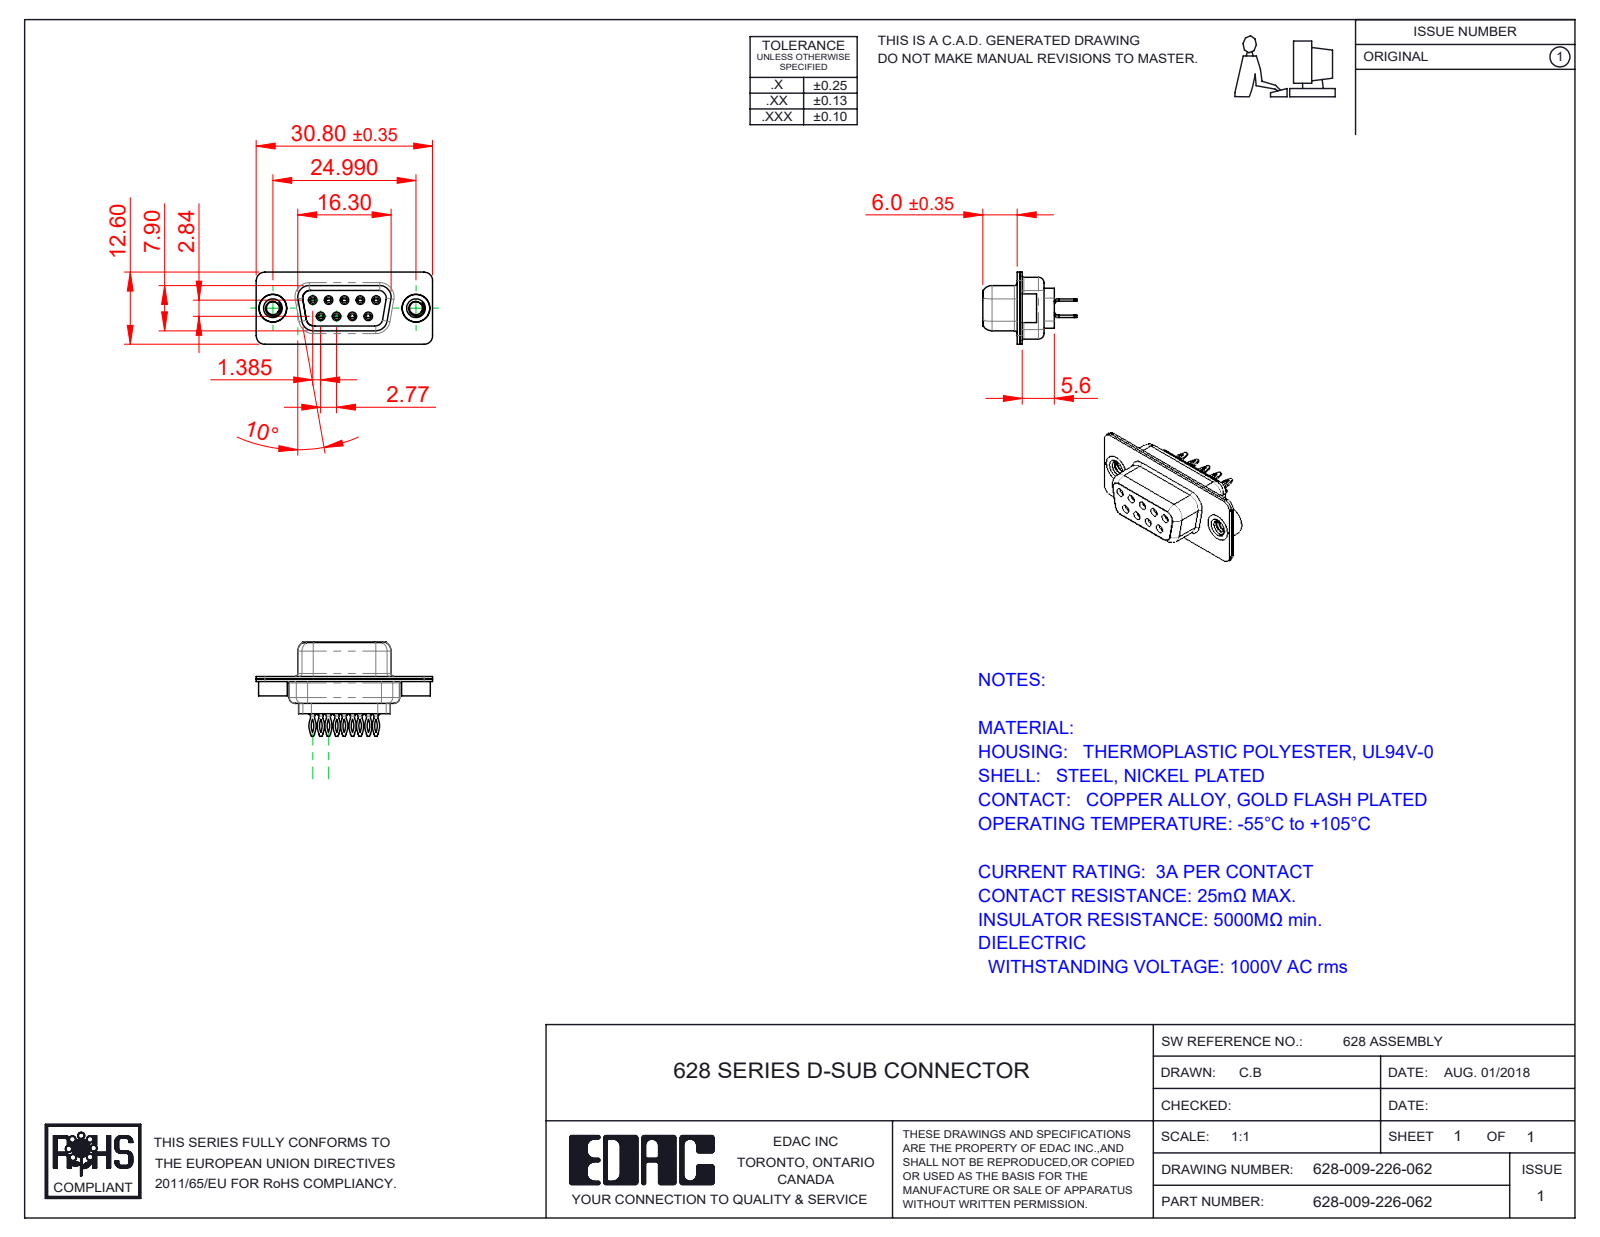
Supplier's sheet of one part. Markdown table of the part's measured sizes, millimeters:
| quantity | value |
| --- | --- |
| part name | 628 Shell Rear_09 Contacts; 628 Contact Row 1_26L; 628 Shell Front_09 Contacts; 628 4-40 Threaded Rivet (+3 more) |
| STEP written by | SolidWorks 2020 (CONFIG_CONTROL_DESIGN) |
| units | millimeters |
| bodies | 14 solids, 1184 faces (310 planar, 378 cylindrical, 496 other) |
| overall size | 30.8 × 16.45 × 12.6 |
| volume | 1 753 mm³ |
| surface area | 4 467 mm² |
| round holes (diameter × count) | 0.8 × 9, 0.9 × 9, 1.1 × 9, 1.6 × 9, 1.7 × 5, 2.26 × 2, 4 × 2, 4.05 × 2, 4.85 × 2 |
| round bosses / shafts (diameter × count) | 2 × 9, 1.5 × 9, 1.2 × 9, 5 × 2, 4.95 × 2, 4.8 × 2 |
| partial cylindrical surfaces (radius × count) | 2.92 × 18, 3.33 × 18, 1.5 × 17, 2 × 12, 0.28 × 9, 1.35 × 6, 0.25 × 4, 0.5 × 4 |
| main face-to-face distances | 0.45, 0.4, 0.9, 1.9, 8.5, 6.6, 1.4, 0.5, 7.05, 0.85 |
| hole center spacings | 3.16, 2.77, 5.54, 5.03, 5.04, 8.31, 7.48, 7.49 |
